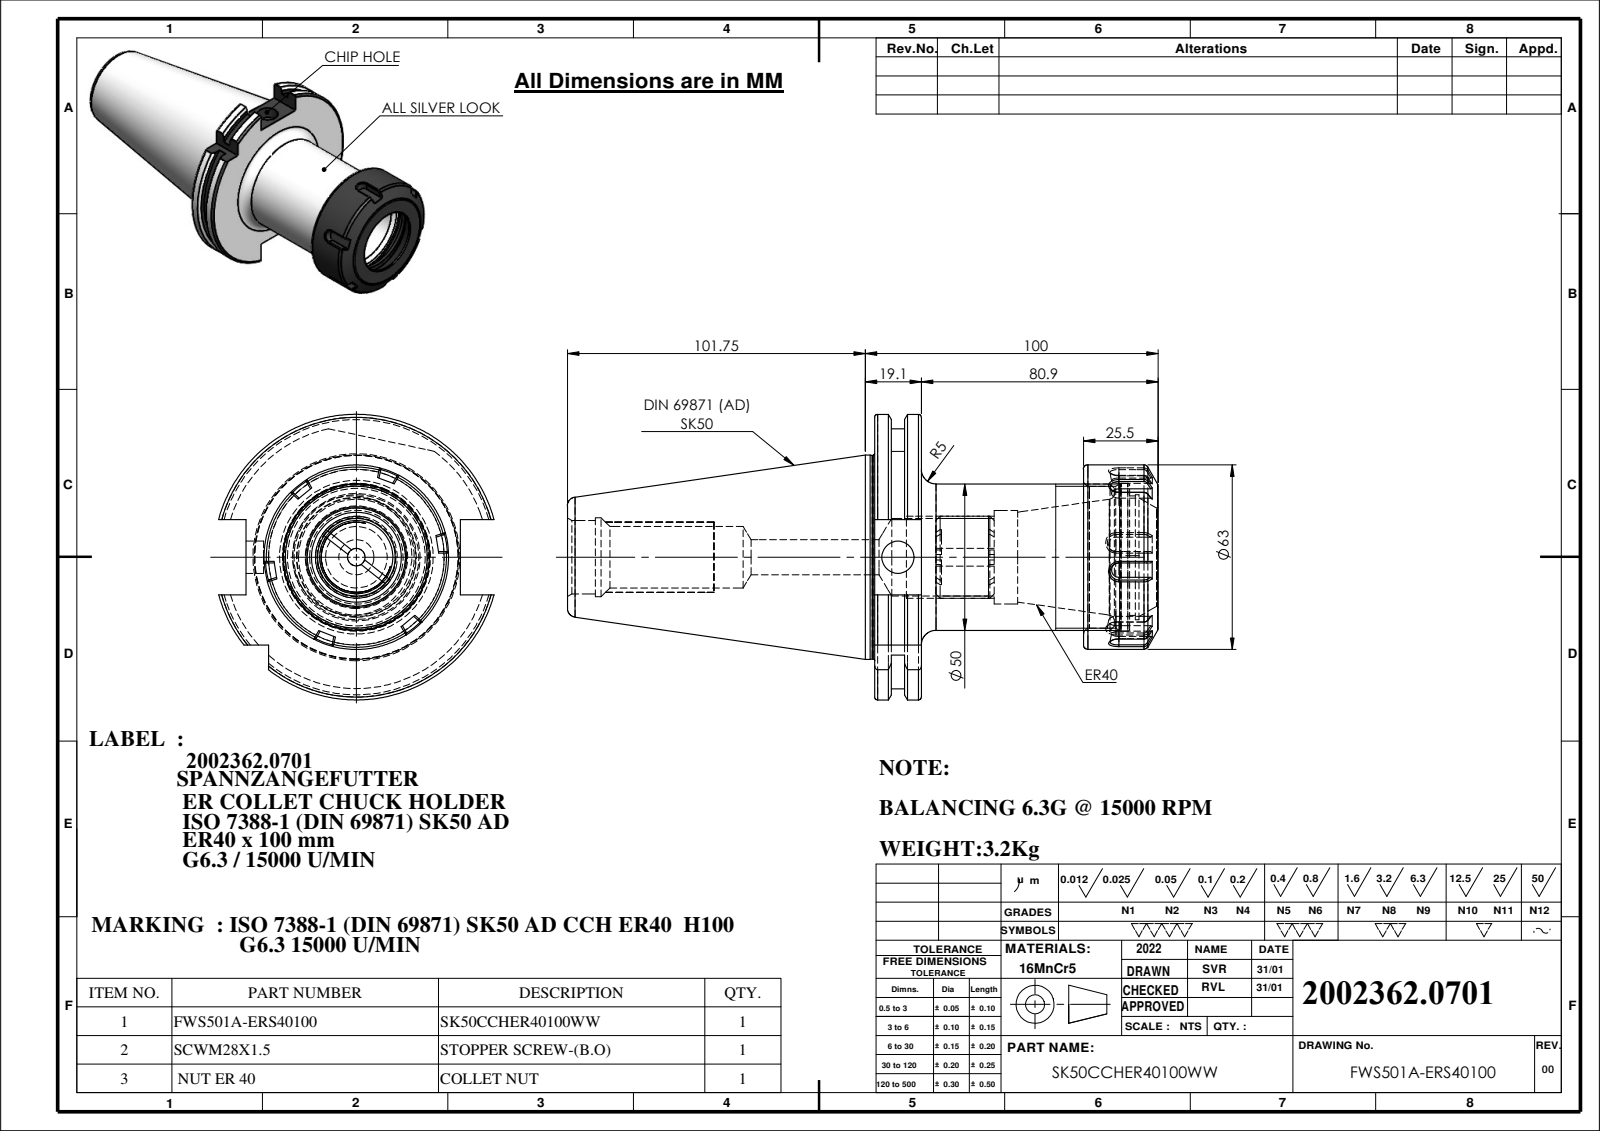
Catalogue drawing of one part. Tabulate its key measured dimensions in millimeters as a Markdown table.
| quantity | value |
| --- | --- |
| part name | SK50CCHER40100WW; 91506-ER140100; FT NUT ER 40; FTSCWM28X150. |
| STEP written by | SolidWorks 2018 (CONFIG_CONTROL_DESIGN) |
| units | millimeters |
| bodies | 3 solids, 230 faces (75 planar, 47 cylindrical, 108 other) |
| overall size | 201.75 × 97.5 × 94.05 |
| volume | 450 322 mm³ |
| surface area | 75 001 mm² |
| round holes (diameter × count) | 6 × 1, 11 × 1, 12 × 1, 21 × 1, 25 × 1, 26.5 × 1, 27 × 1, 32 × 1, 40.75 × 1, 42.6 × 1, 48.5 × 1, 50.5 × 1 |
| round bosses / shafts (diameter × count) | 69.85 × 1, 69.45 × 1, 63 × 1, 50 × 1, 28 × 1 |
| partial cylindrical surfaces (radius × count) | 44.9 × 1, 48.75 × 1 |
| main face-to-face distances | 15.9, 96.8, 80.9, 40.8, 24.9, 56, 71.3, 55.4, 30.5, 25.5 |
| hole center spacings | 1.5 |
